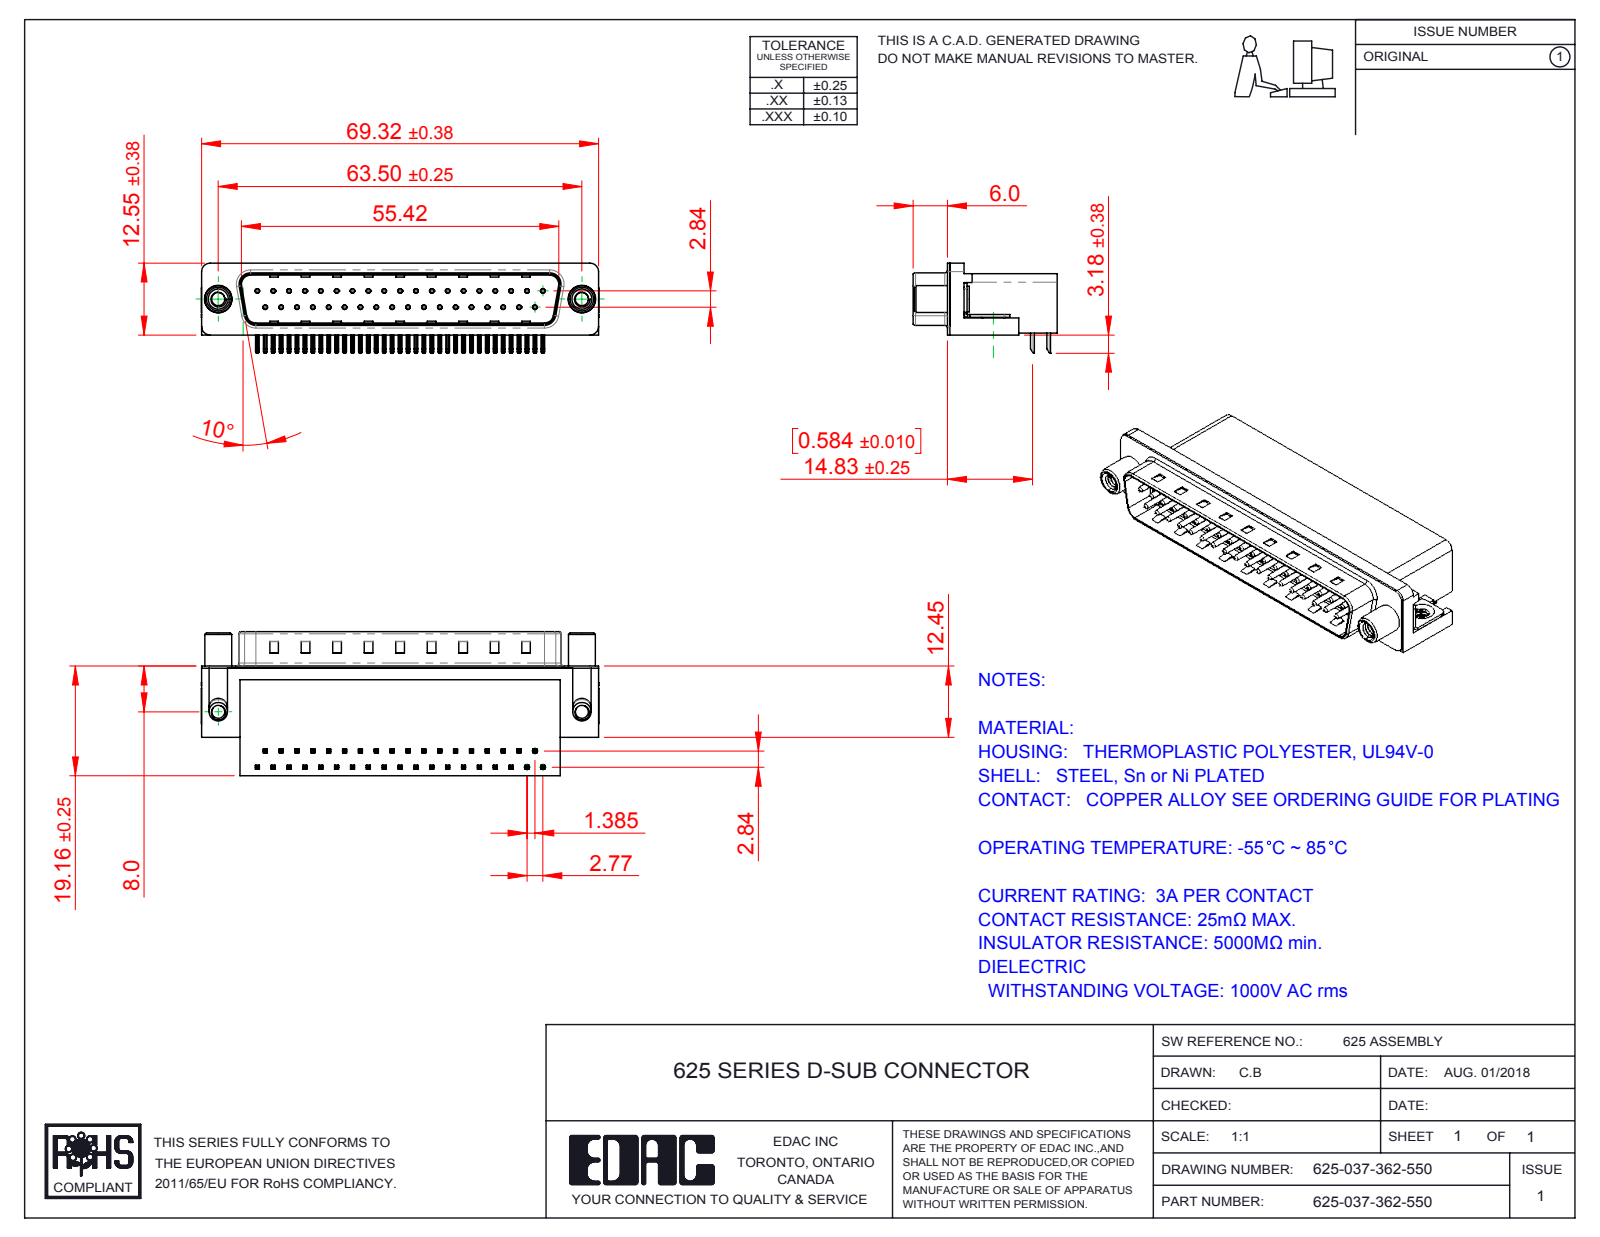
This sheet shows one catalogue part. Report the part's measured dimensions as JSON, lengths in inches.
{"part_name": "625 Round Threaded Standoff; 625-037-362-550; 625 Contact Bottom; 625 Housing_37 Socket (+3 more)", "step_written_by": "SolidWorks 2016 (CONFIG_CONTROL_DESIGN)", "units": "inches", "bodies": {"solids": 43, "faces": 3227, "planar": 2007, "cylindrical": 937, "other": 283}, "overall_size": [2.732, 0.991, 0.619], "volume_in3": 0.775, "surface_area_in2": 18.65, "round_holes": [[0.014, 37], [0.031, 37], [0.089, 2], [0.091, 2], [0.122, 2], [0.157, 2], [0.189, 2], [0.197, 2]], "round_bosses_or_shafts": [[0.03, 37], [0.193, 2], [0.185, 2], [0.177, 2], [0.152, 2], [0.128, 2]], "partial_cylinders_radius": [[0.01, 148], [0.005, 74], [0.039, 16], [0.02, 9], [0.063, 8], [0.059, 7], [0.035, 4], [0.079, 4]], "face_to_face_distances": [0.407, 0.016, 0.739, 0.345, 0.112, 0.754, 0.082, 0.398, 0.069, 0.329], "hole_center_spacings": [0.124, 0.109, 0.218, 0.327, 0.436, 0.545, 0.763, 0.872]}
